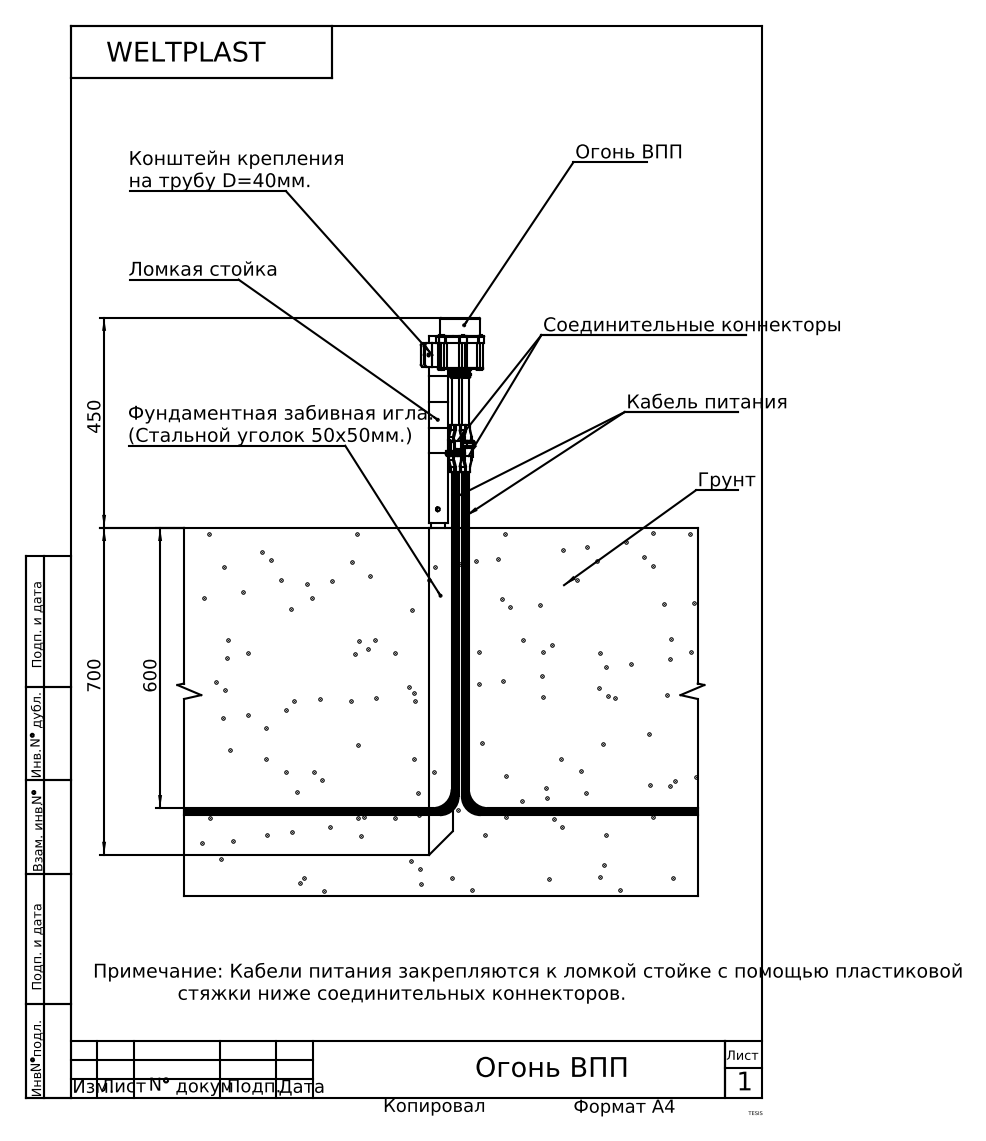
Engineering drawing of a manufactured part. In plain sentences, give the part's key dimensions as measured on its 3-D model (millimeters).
The part is named "конектор зажим; LLC-AP-8; socket button head cap screw_am_B18.3.4M - 4 x 0.7 x 10 SBHCS --S; Сборка_3 (+8 more)". Its 3-D file was written by "SolidWorks 2017 (AUTOMOTIVE_DESIGN)". It is 44 solids with 3014 faces: 887 planar, 1073 cylindrical and 1054 other. Overall it measures 1150 by 145.84 by 136.43 millimeters. Its volume is 890 884 cubic millimeters and its surface area 473 499 square millimeters. Round holes: 8 of diameter 5.3, 6 of diameter 3.6, 6 of diameter 4.4, 6 of diameter 4.5, 5 of diameter 6.3, 3 of diameter 2.5, 3 of diameter 2.62, 2 of diameter 4.2, 2 of diameter 6, 2 of diameter 12.6, 2 of diameter 20.25, 1 of diameter 8.3. Round bosses or shafts: 8 of diameter 7.6, 8 of diameter 4, 2 of diameter 21.5, 2 of diameter 19.7, 2 of diameter 15, 2 of diameter 10.5, 2 of diameter 6, 1 of diameter 85. Partial cylindrical surfaces (rounded edges, fillets, slot ends): 43 of radius 5, 36 of radius 2, 19 of radius 1, 18 of radius 4.5, 14 of radius 1.5, 12 of radius 3, 8 of radius 0.5, 8 of radius 2.5. The main face-to-face distances are 4, 2, 1.5, 3, 9.5, 1, 5.5, 64, 40, 60. The hole center spacings are 47.5, 48.62, 28, 3.47, 58.05, 82.27, 47.51, 95.
